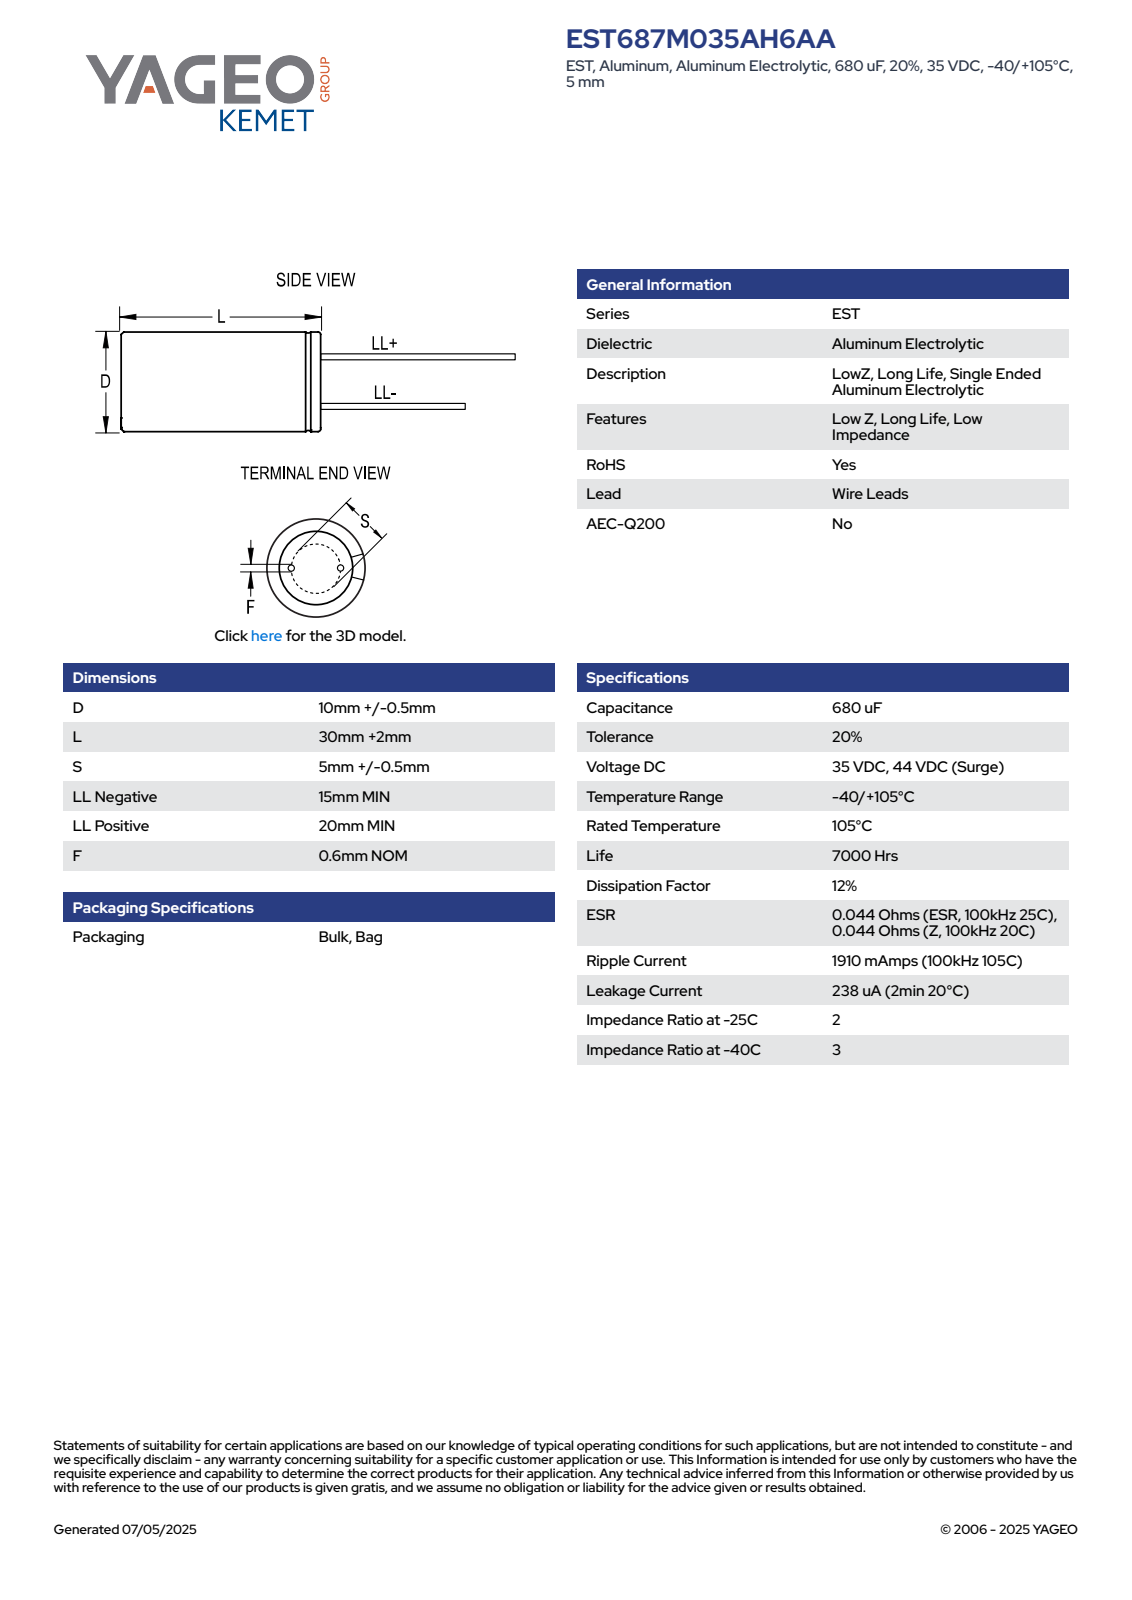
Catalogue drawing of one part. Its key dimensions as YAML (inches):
part_name: "CAR_KLP_10X30_D10.5L32S5F0.6"
step_written_by: "SolidWorks 2014 (AUTOMOTIVE_DESIGN)"
units: inches
bodies: {solids: 4, faces: 75, planar: 61, cylindrical: 8, other: 6}
overall_size: [2.048, 0.413, 0.413]
volume: 0.169
surface_area: 2.044
round_bosses_or_shafts:
  - {diameter: 0.024, count: 2}
  - {diameter: 0.413, count: 1}
face_to_face_distances: [1.26, 1.26, 1.851, 2.048, 1.85, 2.047, 0.591, 0.787, 0.197, 0.056]
